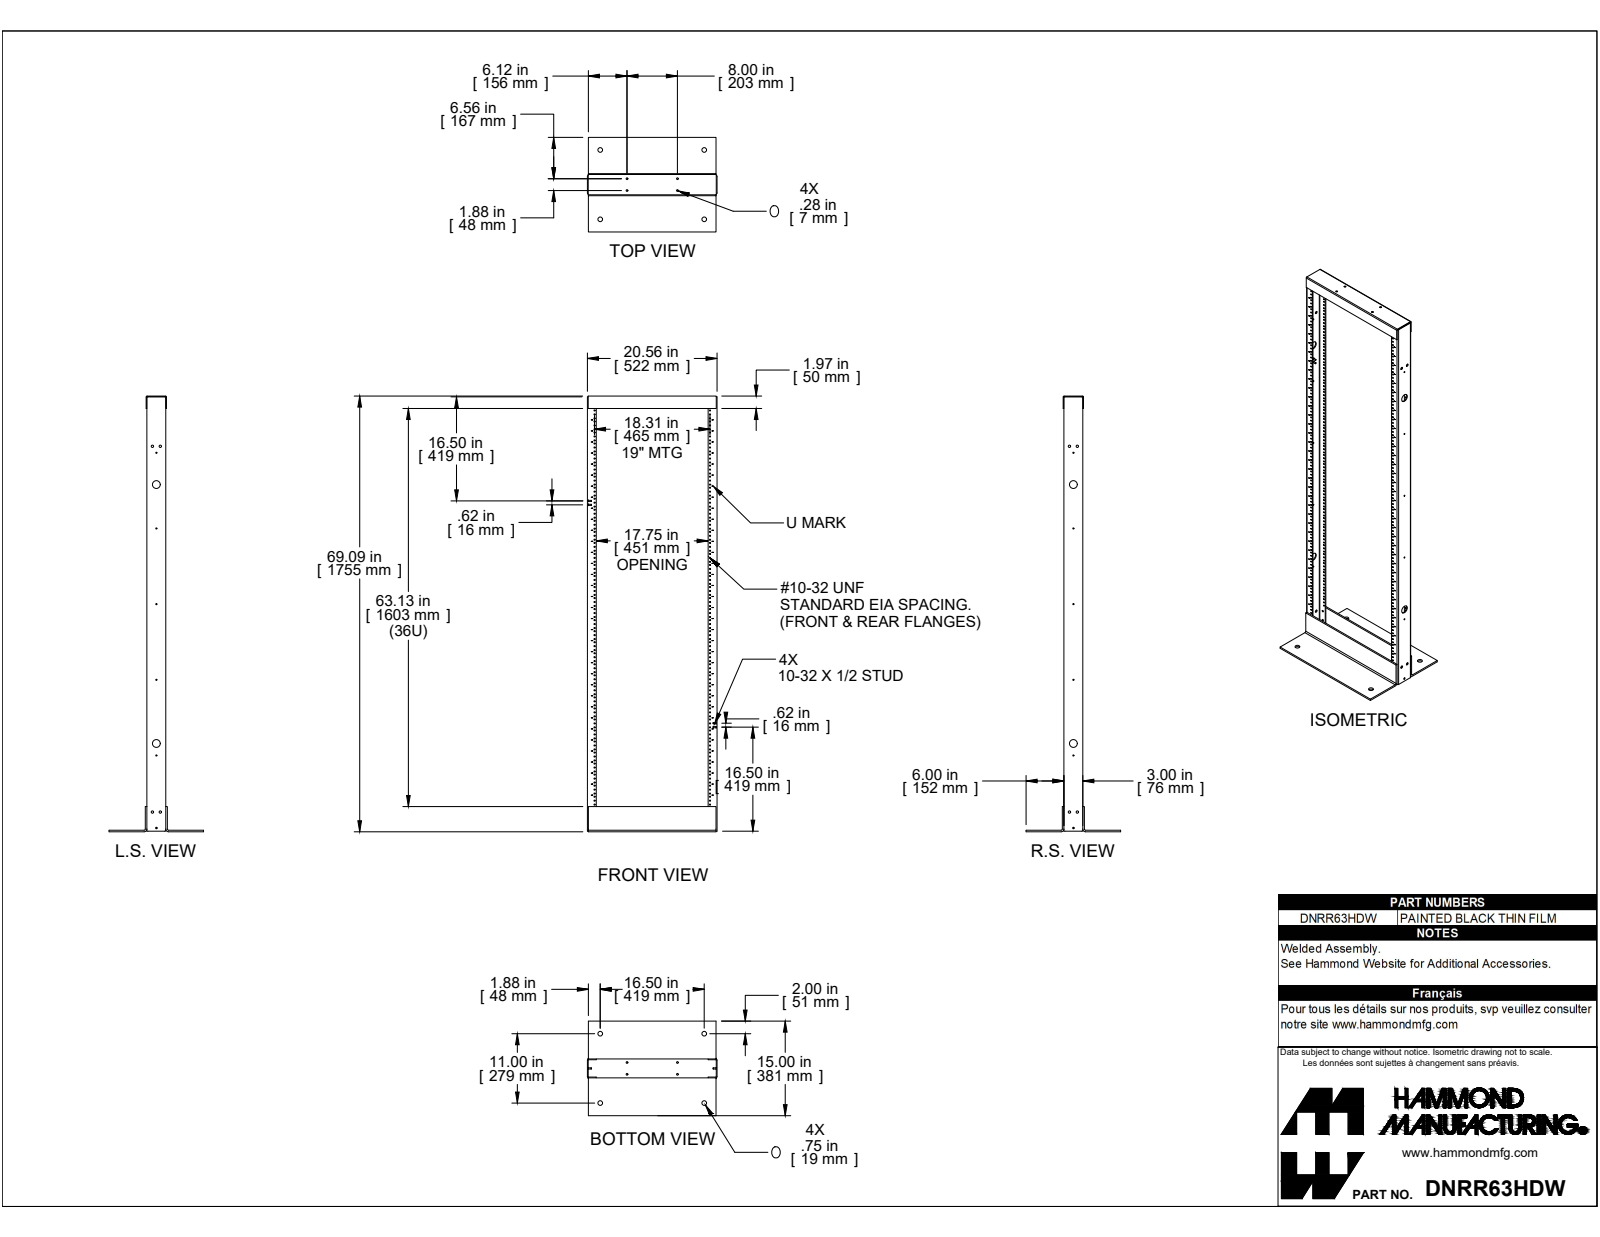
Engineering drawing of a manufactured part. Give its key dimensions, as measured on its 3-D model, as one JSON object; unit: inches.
{"part_name": "DNRR63HDW", "step_written_by": "SolidWorks 2019 (CONFIG_CONTROL_DESIGN)", "units": "inches", "bodies": {"solids": 9, "faces": 1286, "planar": 762, "cylindrical": 520, "other": 4}, "overall_size": [69.094, 20.562, 15], "volume_in3": 201.9, "surface_area_in2": 2637, "round_holes": [[0.177, 227], [0.257, 8], [0.375, 7], [0.281, 4], [0.75, 4], [1.25, 2], [0.25, 1]], "round_bosses_or_shafts": [[0.25, 4], [0.188, 4]], "partial_cylinders_radius": [[0.06, 4], [0.185, 4], [0.048, 2], [0.109, 2], [0.143, 2], [0.188, 2], [0.438, 2]], "face_to_face_distances": [0.125, 0.25, 0.125, 2.875, 3, 20.437, 20.312, 20.562, 20.437, 0.375], "hole_center_spacings": [1.75, 3.5, 5.25, 7, 8.75, 1.25, 10.5, 0.625]}
